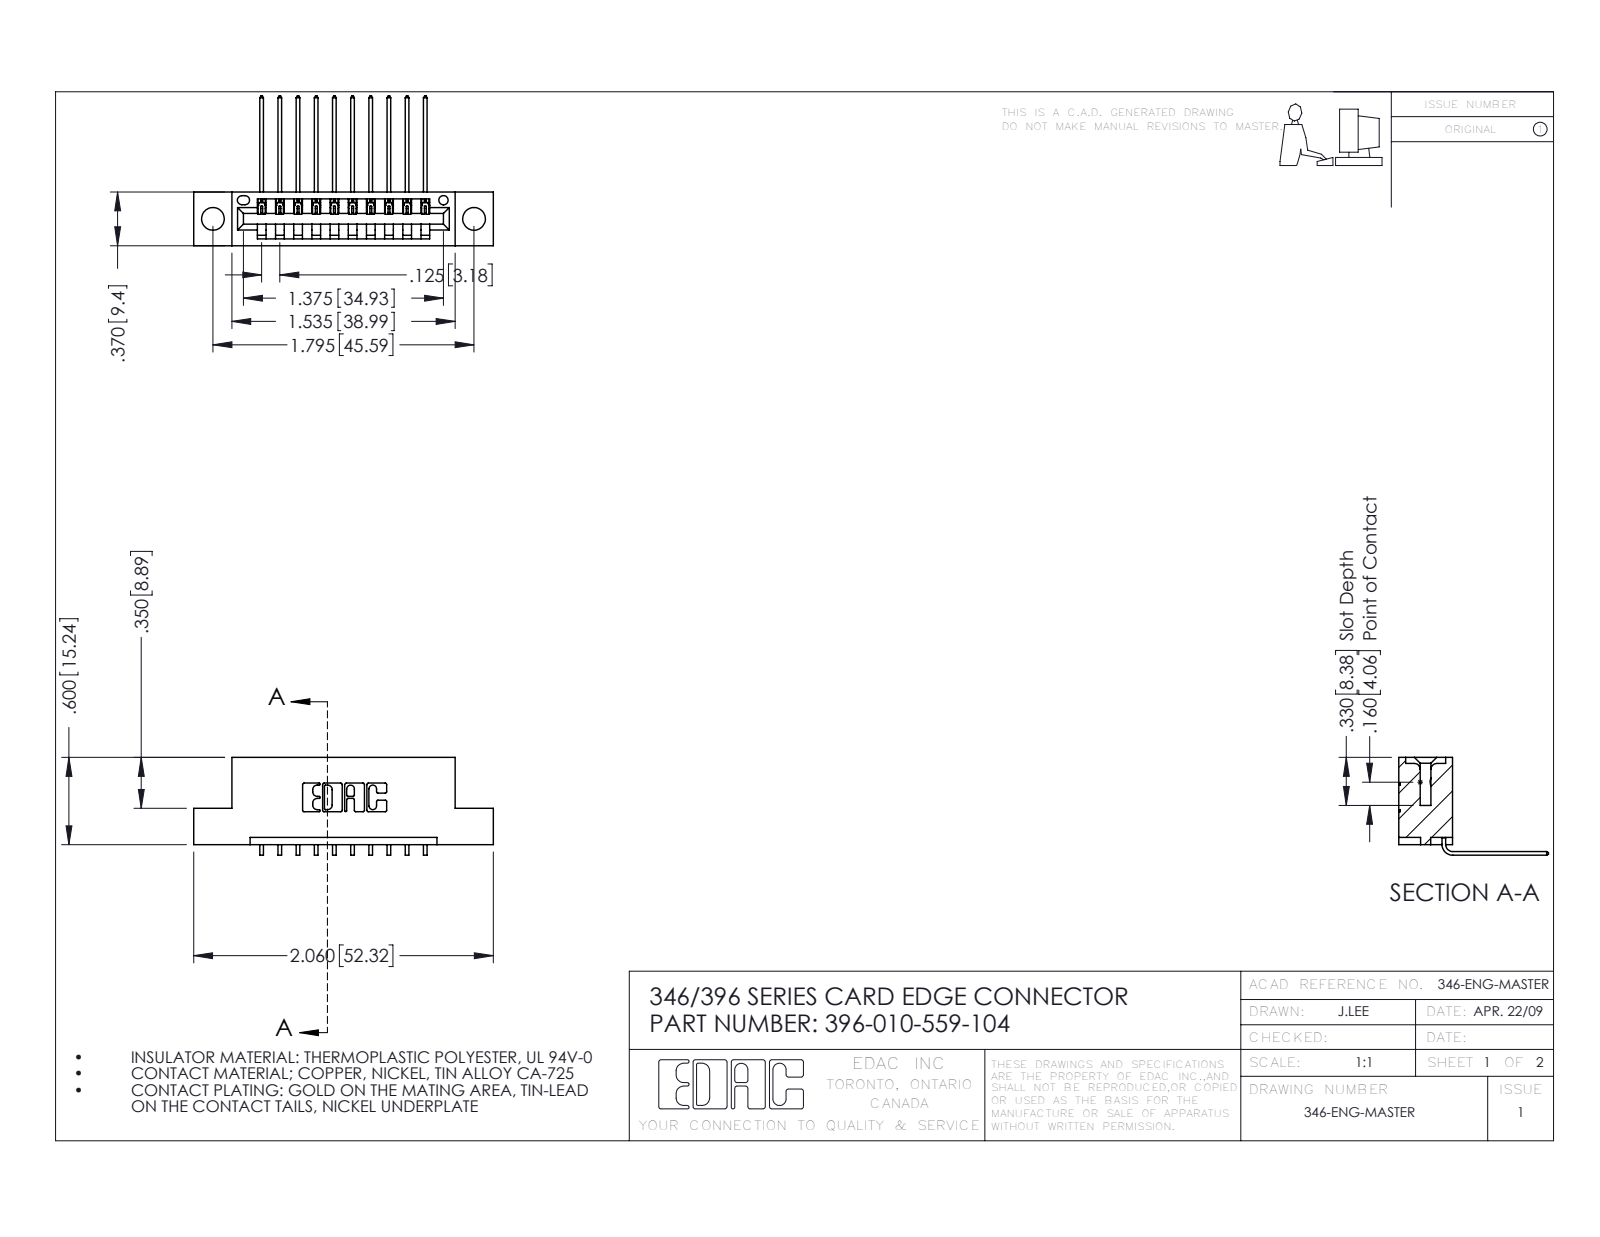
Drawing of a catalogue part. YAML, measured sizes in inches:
part_name: "346 Part_Flush Mounting Lugs - 0.156 Dia-TH; 345-292-001_558 559 Tail - 1; 396-010-559-104"
step_written_by: "SolidWorks 2016 (CONFIG_CONTROL_DESIGN)"
units: inches
bodies: {solids: 11, faces: 722, planar: 496, cylindrical: 226, other: 0}
overall_size: [2.06, 1.03, 0.673]
volume: 0.289
surface_area: 8.641
round_holes:
  - {diameter: 0.156, count: 2}
  - {diameter: 0.064, count: 1}
partial_cylinders:
  - {radius: 0.01, count: 22}
  - {radius: 0.006, count: 20}
  - {radius: 0.007, count: 6}
  - {radius: 0.031, count: 6}
  - {radius: 0.026, count: 3}
  - {radius: 0.031, count: 2}
  - {radius: 0.04, count: 2}
  - {radius: 0.014, count: 1}
face_to_face_distances: [0.25, 0.048, 0.322, 0.37, 0.072, 0.025, 0.298, 0.148, 0.222, 0.1]
hole_center_spacings: [0.246, 1.59, 1.795]
